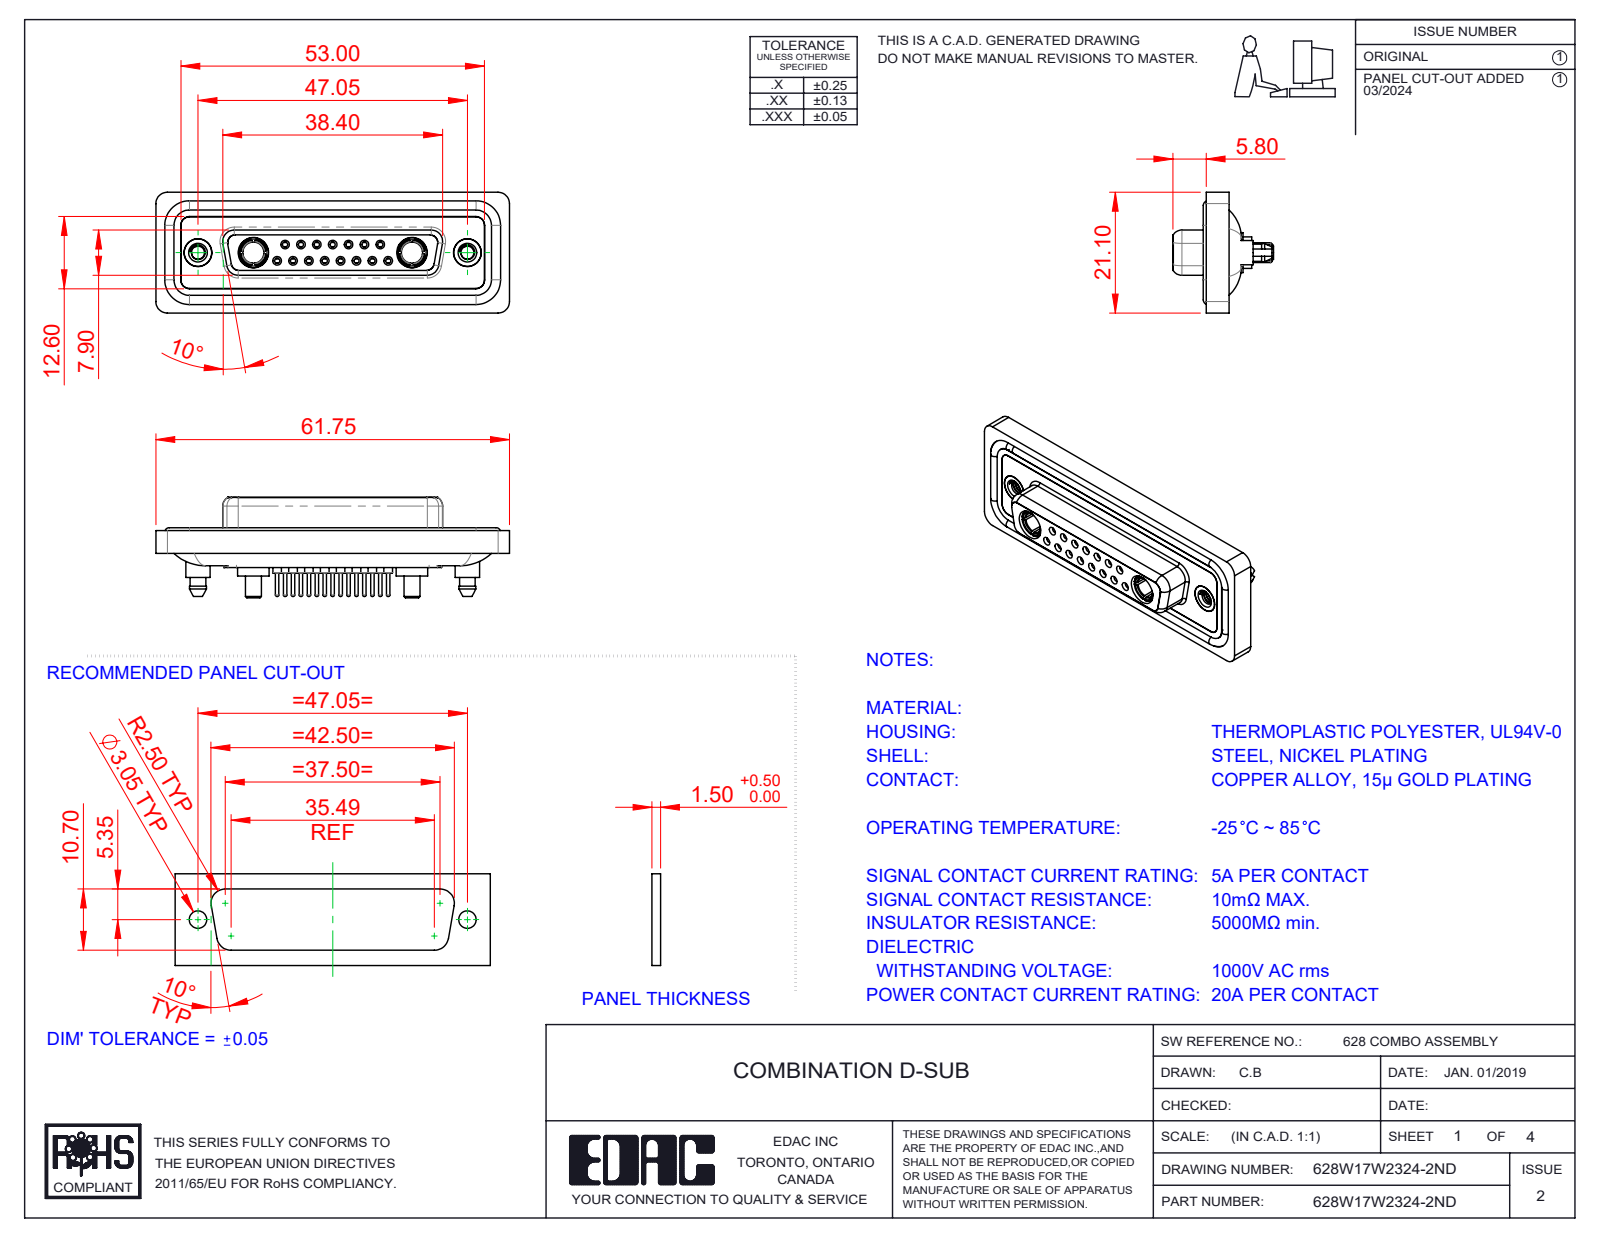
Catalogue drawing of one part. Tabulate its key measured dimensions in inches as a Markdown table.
| quantity | value |
| --- | --- |
| part name | 628Combo Contact Row 1_24; 628Combo Contact Row 2_24; Power Socket_20A S; 628Combo Housing_17W2 (+5 more) |
| STEP written by | SolidWorks 2023 (CONFIG_CONTROL_DESIGN) |
| units | inches |
| bodies | 26 solids, 1425 faces (404 planar, 567 cylindrical, 454 other) |
| overall size | 2.431 × 0.831 × 0.691 |
| volume | 0.516 in³ |
| surface area | 22 in² |
| round holes (diameter × count) | 0.035 × 15, 0.043 × 15, 0.059 × 15, 0.079 × 15, 0.063 × 8, 0.067 × 7, 0.191 × 4, 0.089 × 2, 0.146 × 2, 0.157 × 2, 0.159 × 2, 0.197 × 2 |
| round bosses / shafts (diameter × count) | 0.087 × 15, 0.024 × 15, 0.063 × 11, 0.217 × 2, 0.213 × 2, 0.205 × 2, 0.195 × 2, 0.195 × 2 |
| partial cylindrical surfaces (radius × count) | 0.059 × 24, 0.079 × 18, 0.063 × 10, 0.053 × 8, 0.01 × 4, 0.02 × 4, 0.024 × 4, 0.026 × 4 |
| main face-to-face distances | 0.016, 0.071, 0.293, 0.222, 0.26, 0.02, 0.278, 0.063, 0.114, 0.043 |
| hole center spacings | 0.124, 0.109, 0.327, 0.218, 0.198, 0.198, 0.295, 0.436 |
